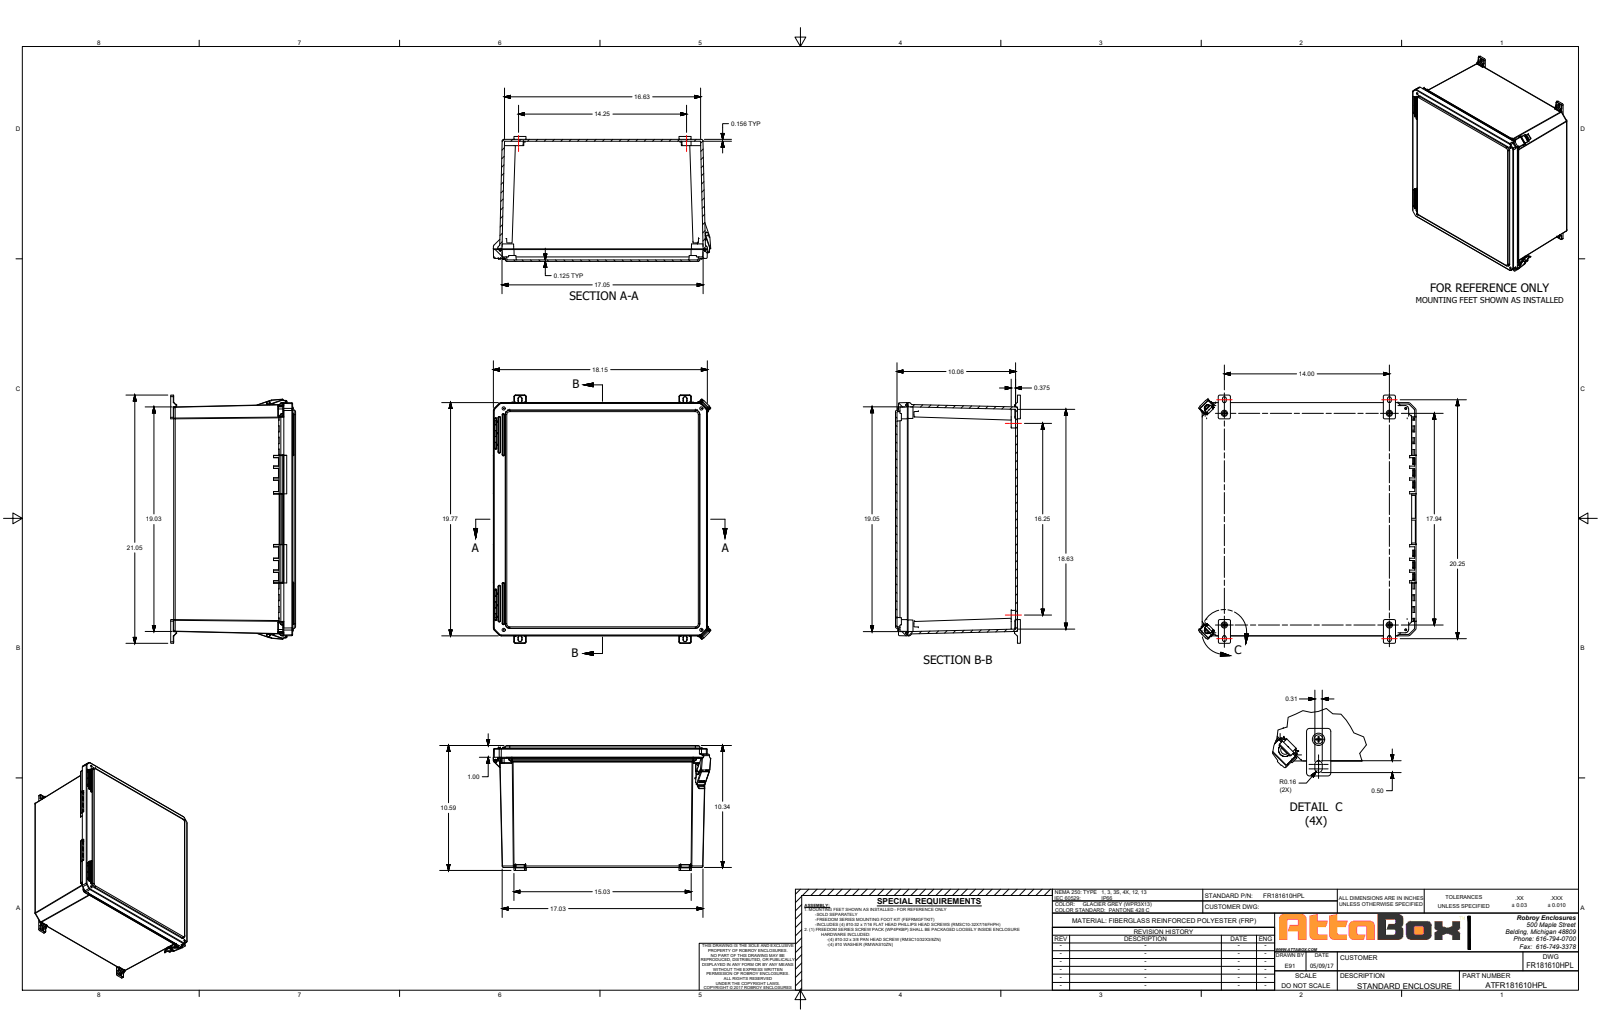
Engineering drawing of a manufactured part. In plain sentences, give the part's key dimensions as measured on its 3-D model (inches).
The part is named "FR181610HPL". Its 3-D file was written by "SolidWorks 2021 (AUTOMOTIVE_DESIGN)". It is 29 solids with 2495 faces: 812 planar, 1062 cylindrical and 621 other. Overall it measures 20.348 by 18.432 by 10.911 inches. Its volume is 259.6 cubic inches and its surface area 2 971 square inches. Round holes: 8 of diameter 0.152, 8 of diameter 0.159, 5 of diameter 0.135, 4 of diameter 0.135, 4 of diameter 0.15, 4 of diameter 0.156, 4 of diameter 0.252, 4 of diameter 0.253, 3 of diameter 0.137, 2 of diameter 0.219, 2 of diameter 0.227, 2 of diameter 0.313. Round bosses or shafts: 8 of diameter 0.27, 4 of diameter 0.3, 4 of diameter 0.262, 4 of diameter 0.209, 3 of diameter 0.135, 2 of diameter 0.435, 1 of diameter 0.135. Partial cylindrical surfaces (rounded edges, fillets, slot ends): 191 of radius 0.01, 110 of radius 0.005, 71 of radius 0.03, 54 of radius 0.02, 36 of radius 0.06, 26 of radius 0.09, 24 of radius 0.03, 24 of radius 0.096. The main face-to-face distances are 0.125, 0.156, 10.182, 10.338, 10.213, 10.057, 0.202, 0.199, 0.202, 0.2. The hole center spacings are 14.15, 16.772, 18.409, 18.77, 1.445, 17.556, 22.177, 17.098.
